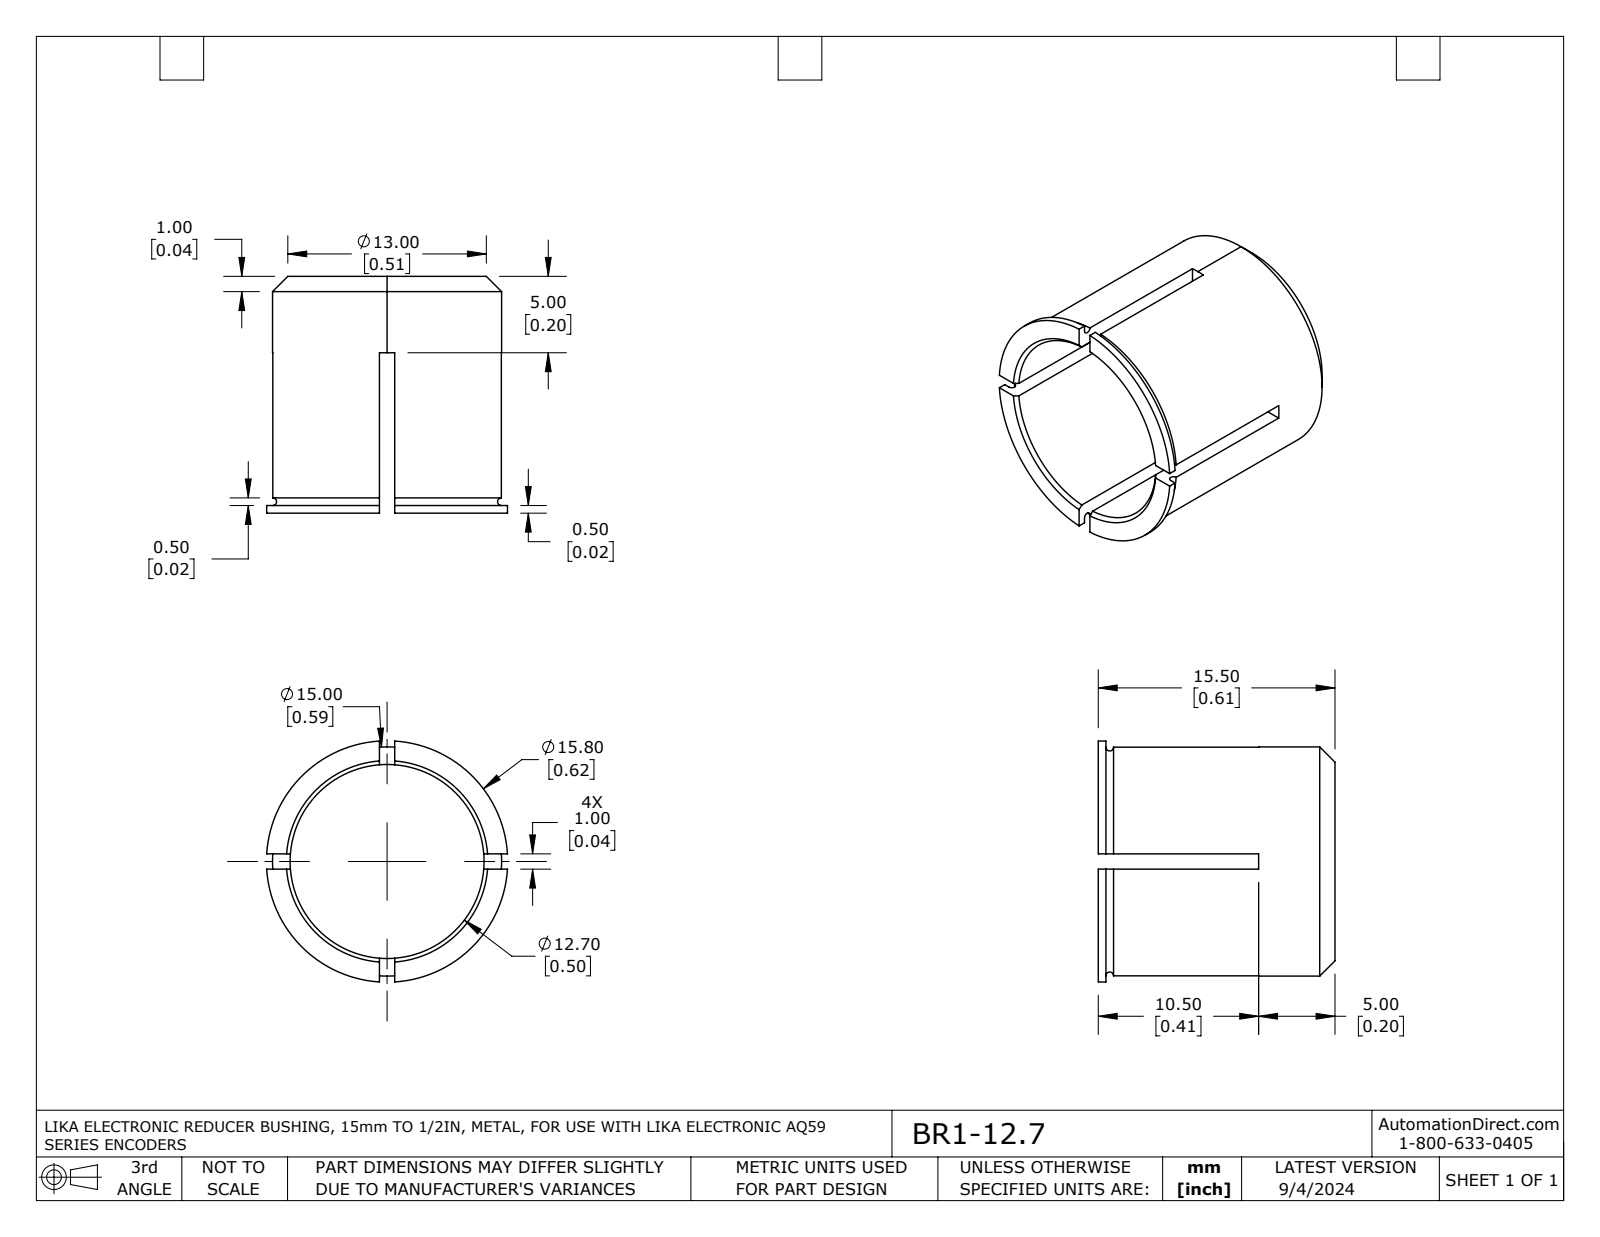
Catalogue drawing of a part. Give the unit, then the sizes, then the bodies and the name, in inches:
Units: inches
Overall size (bounding box): 0.621 × 0.621 × 0.61
Round holes (diameter × count): ⌀0.5 ×1
Round bosses / shafts (diameter × count): ⌀0.622 ×1, ⌀0.591 ×1
Main face-to-face distances: 0.039, 0.02, 0.591, 0.61, 0.197, 0.394, 0.413
Volume: 0.043 in³ · Surface area: 2.289 in²
Bodies: 1 solid, 42 faces (21 planar, 10 cylindrical, 11 other)
Part name (STEP PRODUCT): BR1-12,7
STEP written by: SolidWorks 2021 (AUTOMOTIVE_DESIGN)
